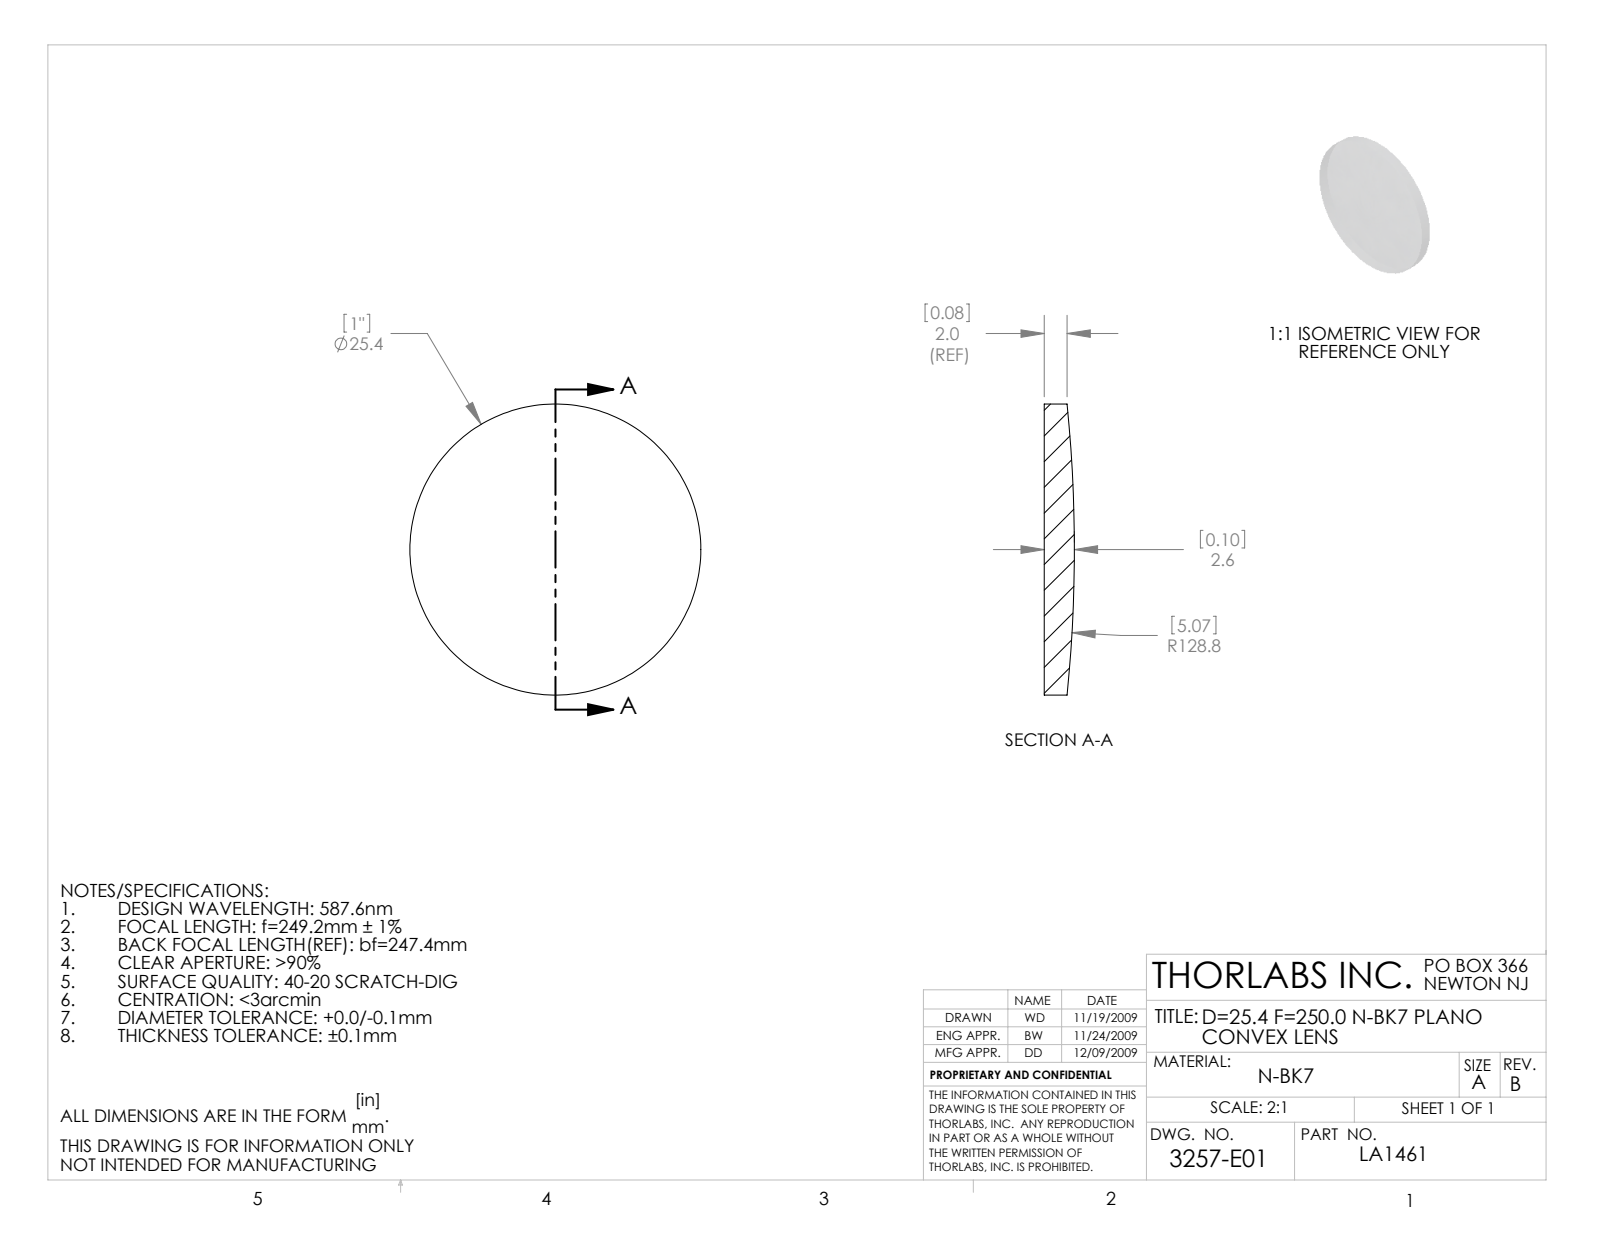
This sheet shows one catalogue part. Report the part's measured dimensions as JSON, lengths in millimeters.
{"part_name": "3257-E0W", "step_written_by": "SolidWorks 2009 (AUTOMOTIVE_DESIGN)", "units": "millimeters", "bodies": {"solids": 1, "faces": 5, "planar": 1, "cylindrical": 2, "other": 2}, "overall_size": [25.4, 25.4, 2.62], "volume_mm3": 1169, "surface_area_mm2": 1174, "round_bosses_or_shafts": [[25.4, 1]]}
